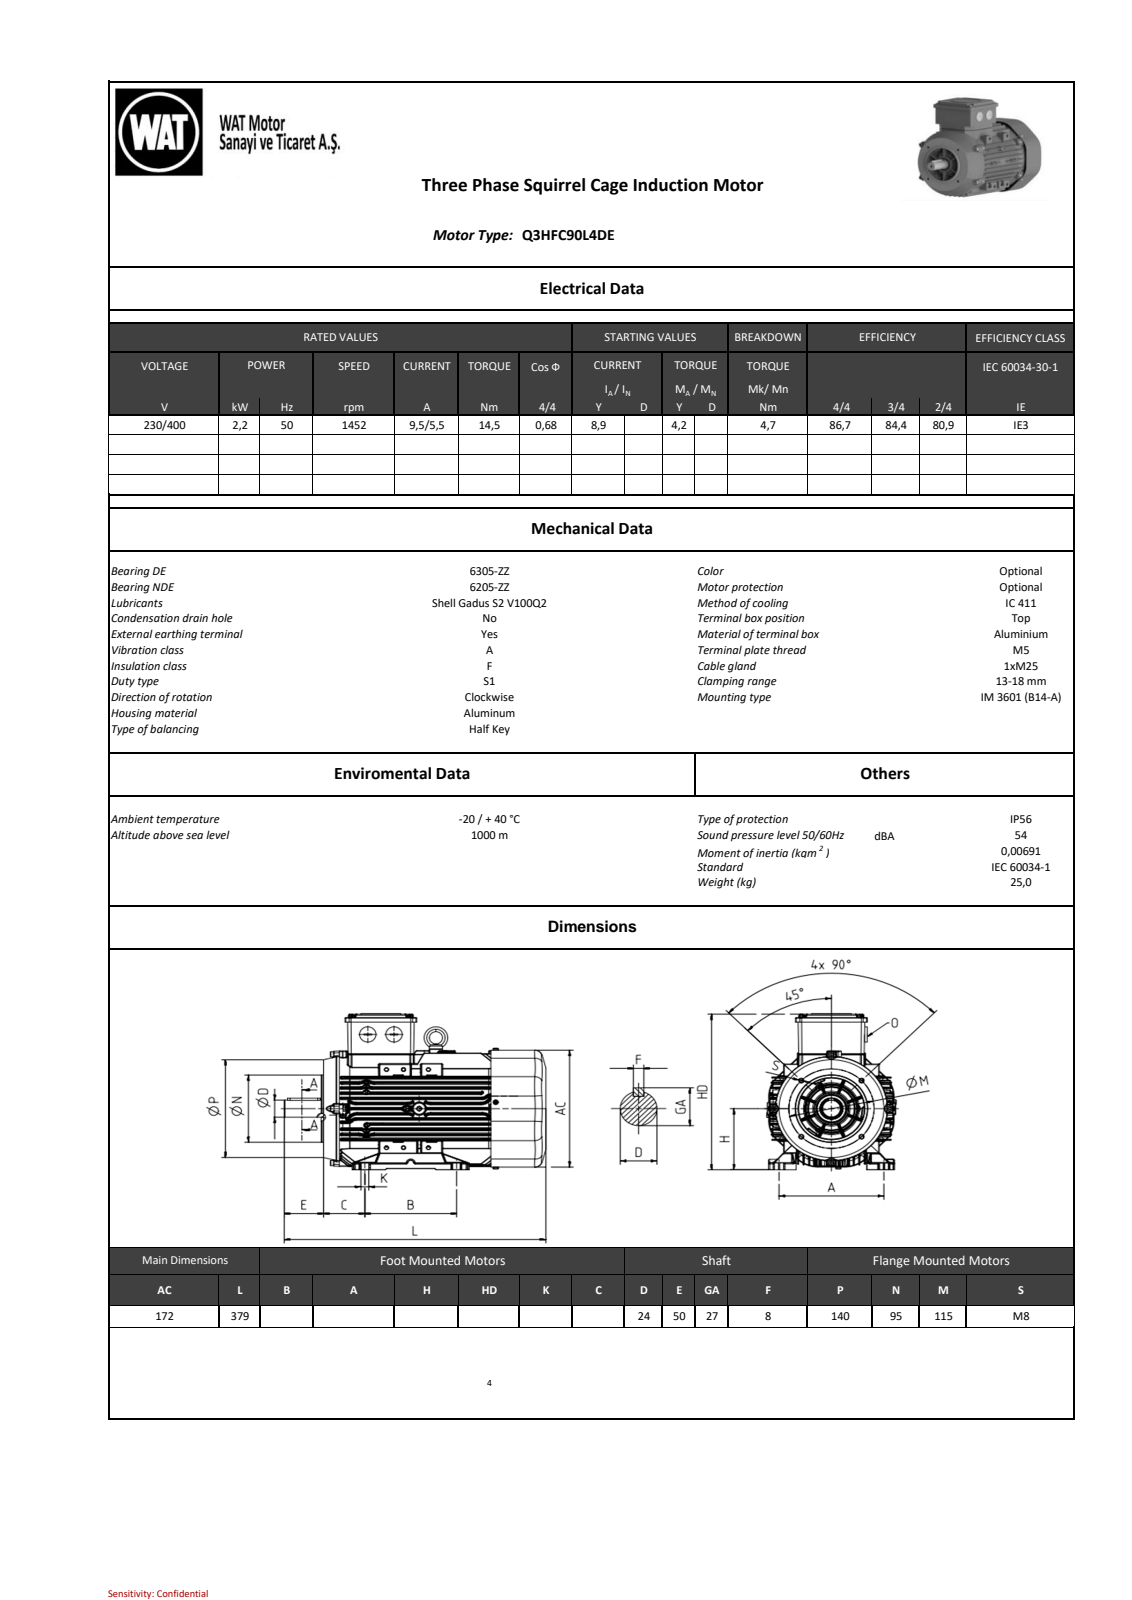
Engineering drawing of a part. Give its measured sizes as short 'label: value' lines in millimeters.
name: model1
written by: SIEMENS PLM Software NX2206.8101 (AUTOMOTIVE_DESIGN)
unit: mm
bodies: 0 solids, 6024 faces (1498 planar, 2096 cylindrical, 2430 other)
size: 378.54 × 219.15 × 172.19
holes: 4× ⌀6.8, 1× ⌀8.4, 1× ⌀9.87, 1× ⌀40, 1× ⌀79.79, 1× ⌀97.79, 1× ⌀115.78
bosses: 7× ⌀8, 5× ⌀5, 3× ⌀25, 2× ⌀10, 1× ⌀102.19, 1× ⌀95, 1× ⌀84.19, 1× ⌀37.42
rounds: 620× R0.8, 408× R1, 159× R0.5, 63× R2, 28× R8, 20× R0.5, 10× R4, 4× R0.7
face distances: 7.5, 91.91, 8.93, 82.98, 23.57, 50.35, 1.25, 7.37, 90.35, 16.87
hole spacings: 57.51, 81.33, 57.47, 57.54, 115.02
